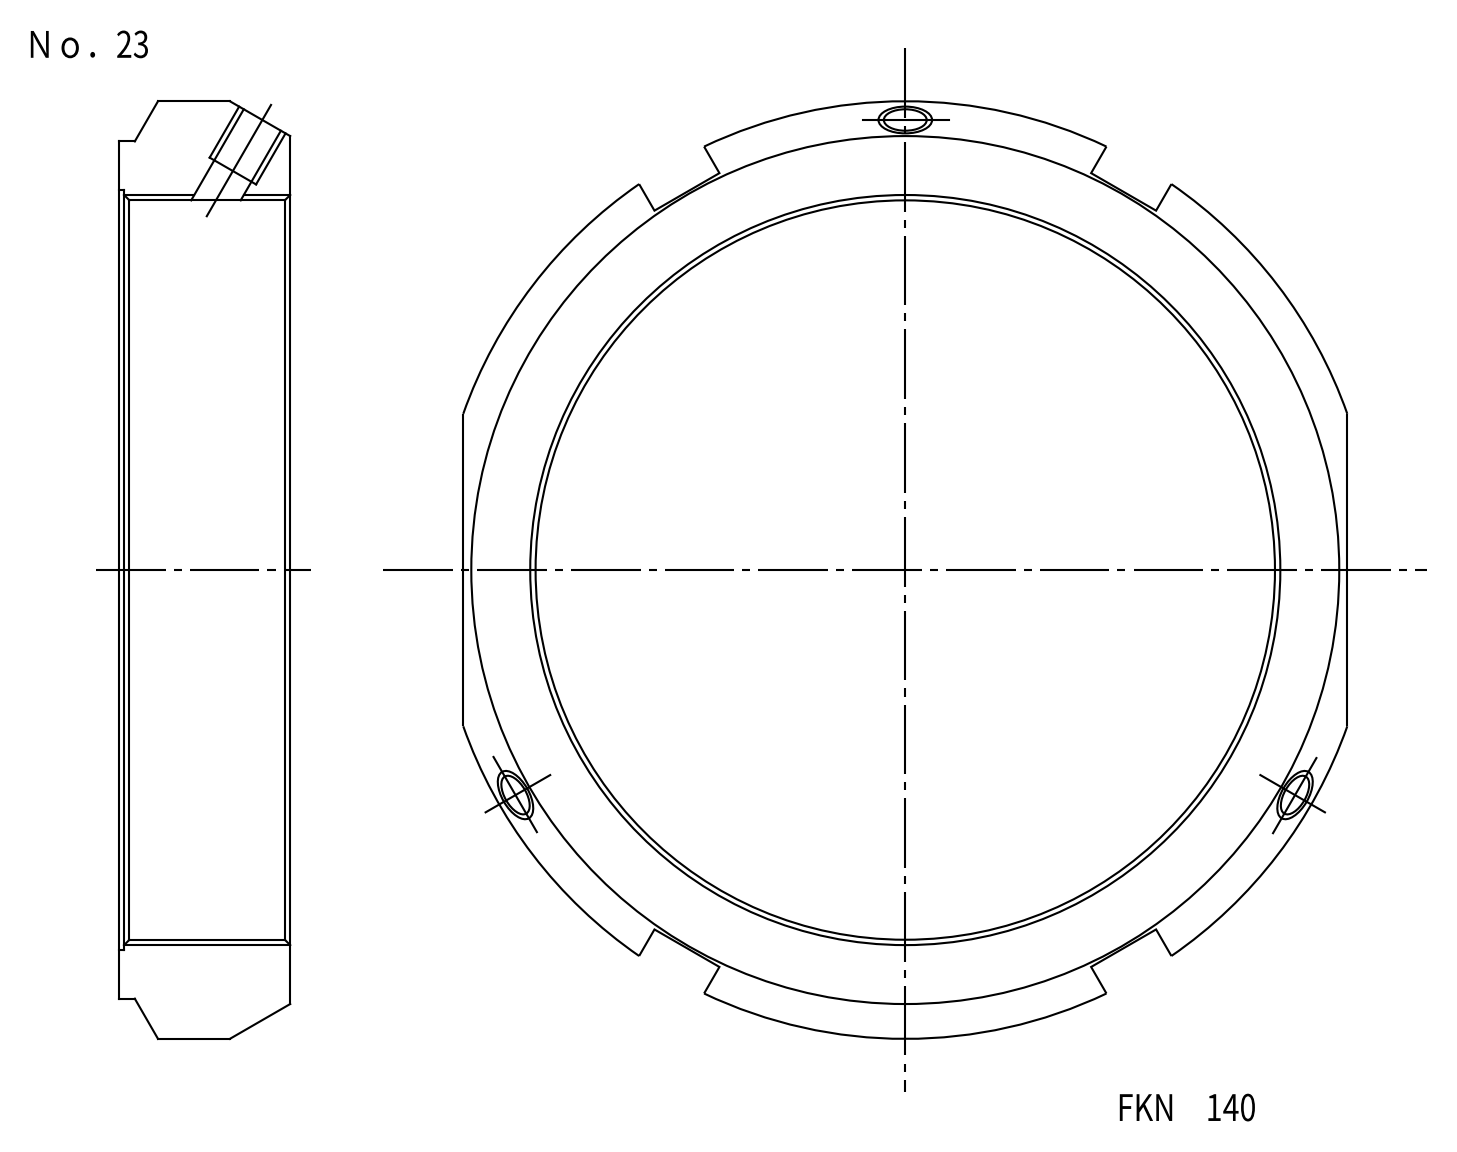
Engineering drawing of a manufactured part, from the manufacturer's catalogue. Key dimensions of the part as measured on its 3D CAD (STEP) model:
Part name (STEP PRODUCT): FKD FKN140
STEP written by: Autodesk Inventor LT (CONFIG_CONTROL_DESIGN)
Units: millimetres
Bodies: 1 solid, 37 faces (20 planar, 15 cylindrical, 2 other)
Overall size (bounding box): 175 × 165 × 32
Volume: 219 891 mm³ · Surface area: 45 513 mm²
Round holes (diameter × count): ⌀8.38 ×3, ⌀10.2 ×3, ⌀140 ×1, ⌀142 ×1
Round bosses / shafts (diameter × count): ⌀160 ×1
Partial cylindrical surfaces — rounded edges, fillets, slot ends (radius × count): R87.5 ×1
Main face-to-face distances: 32, 165, 163, 14, 1.5, 30.5
